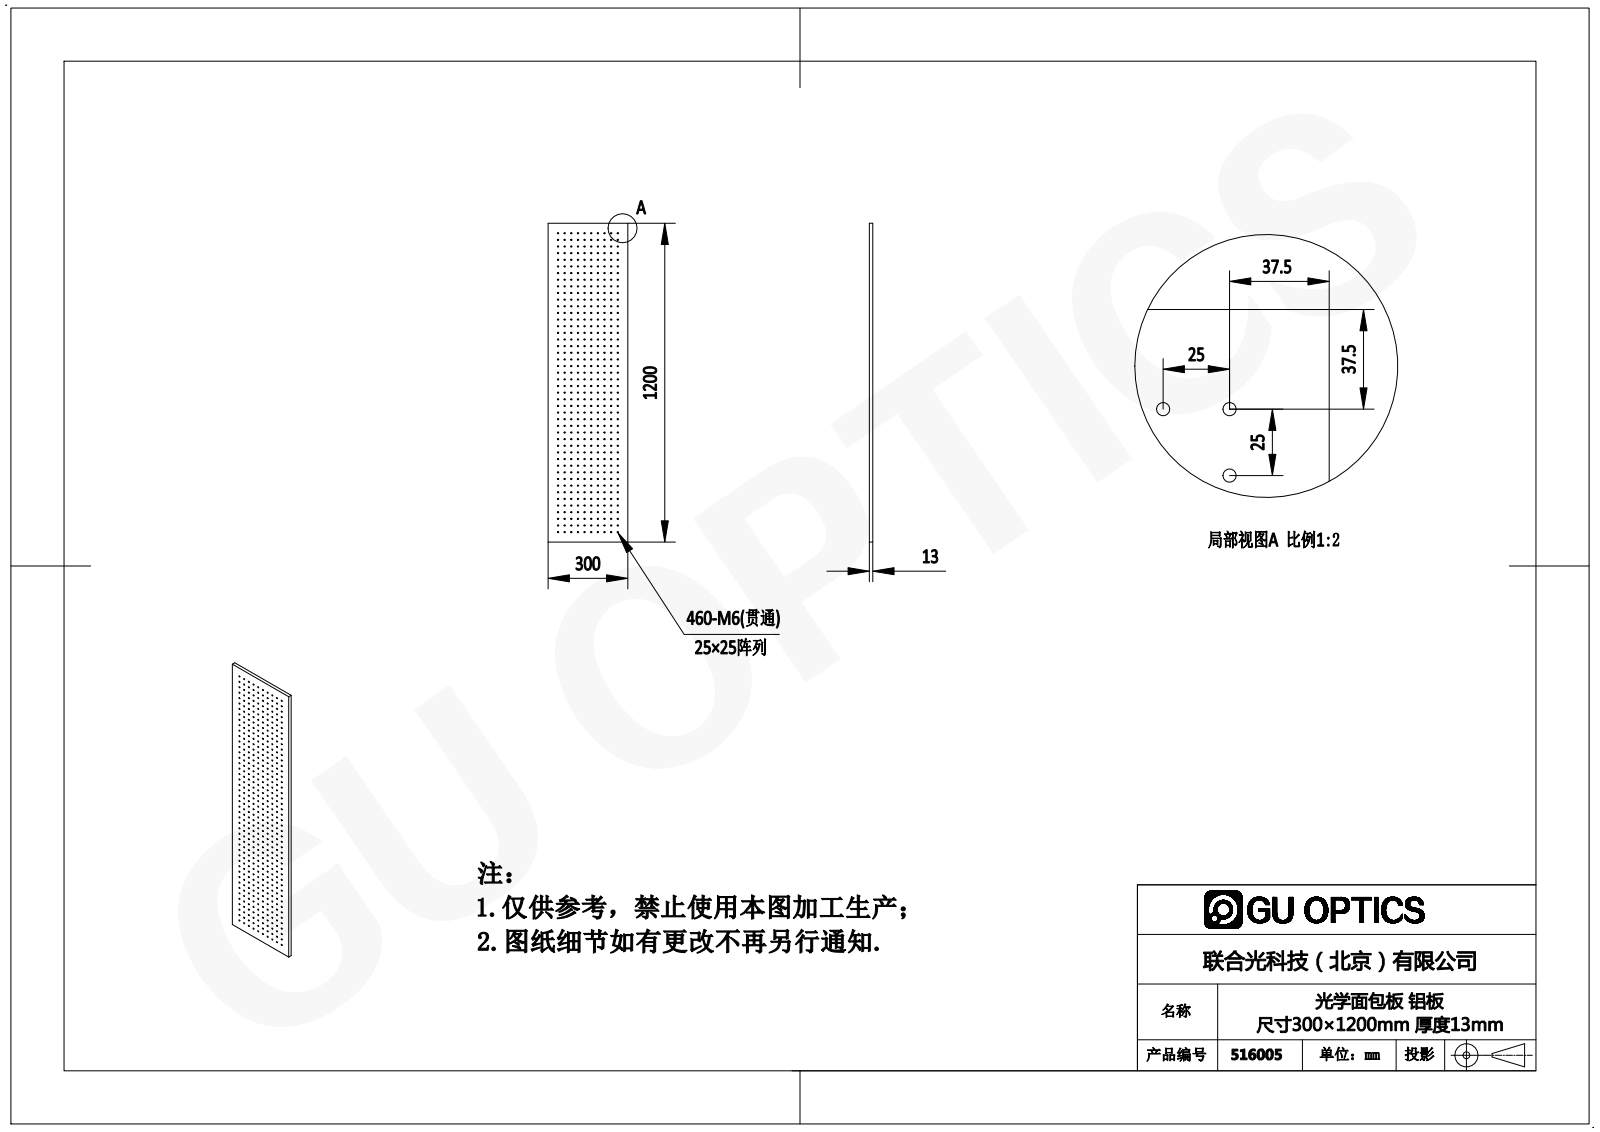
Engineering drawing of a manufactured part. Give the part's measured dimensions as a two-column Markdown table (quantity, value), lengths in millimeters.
| quantity | value |
| --- | --- |
| part name | 516005 |
| STEP written by | SolidWorks 2016 (AUTOMOTIVE_DESIGN) |
| units | millimeters |
| bodies | 1 solid, 926 faces (6 planar, 920 cylindrical, 0 other) |
| overall size | 1200 × 300 × 13 |
| volume | 4 563 000 mm³ |
| surface area | 834 869 mm² |
| round holes (diameter × count) | 5 × 460 |
| main face-to-face distances | 13, 300, 1200 |
| hole center spacings | 25, 50, 75, 100, 125, 150, 175, 200 |
